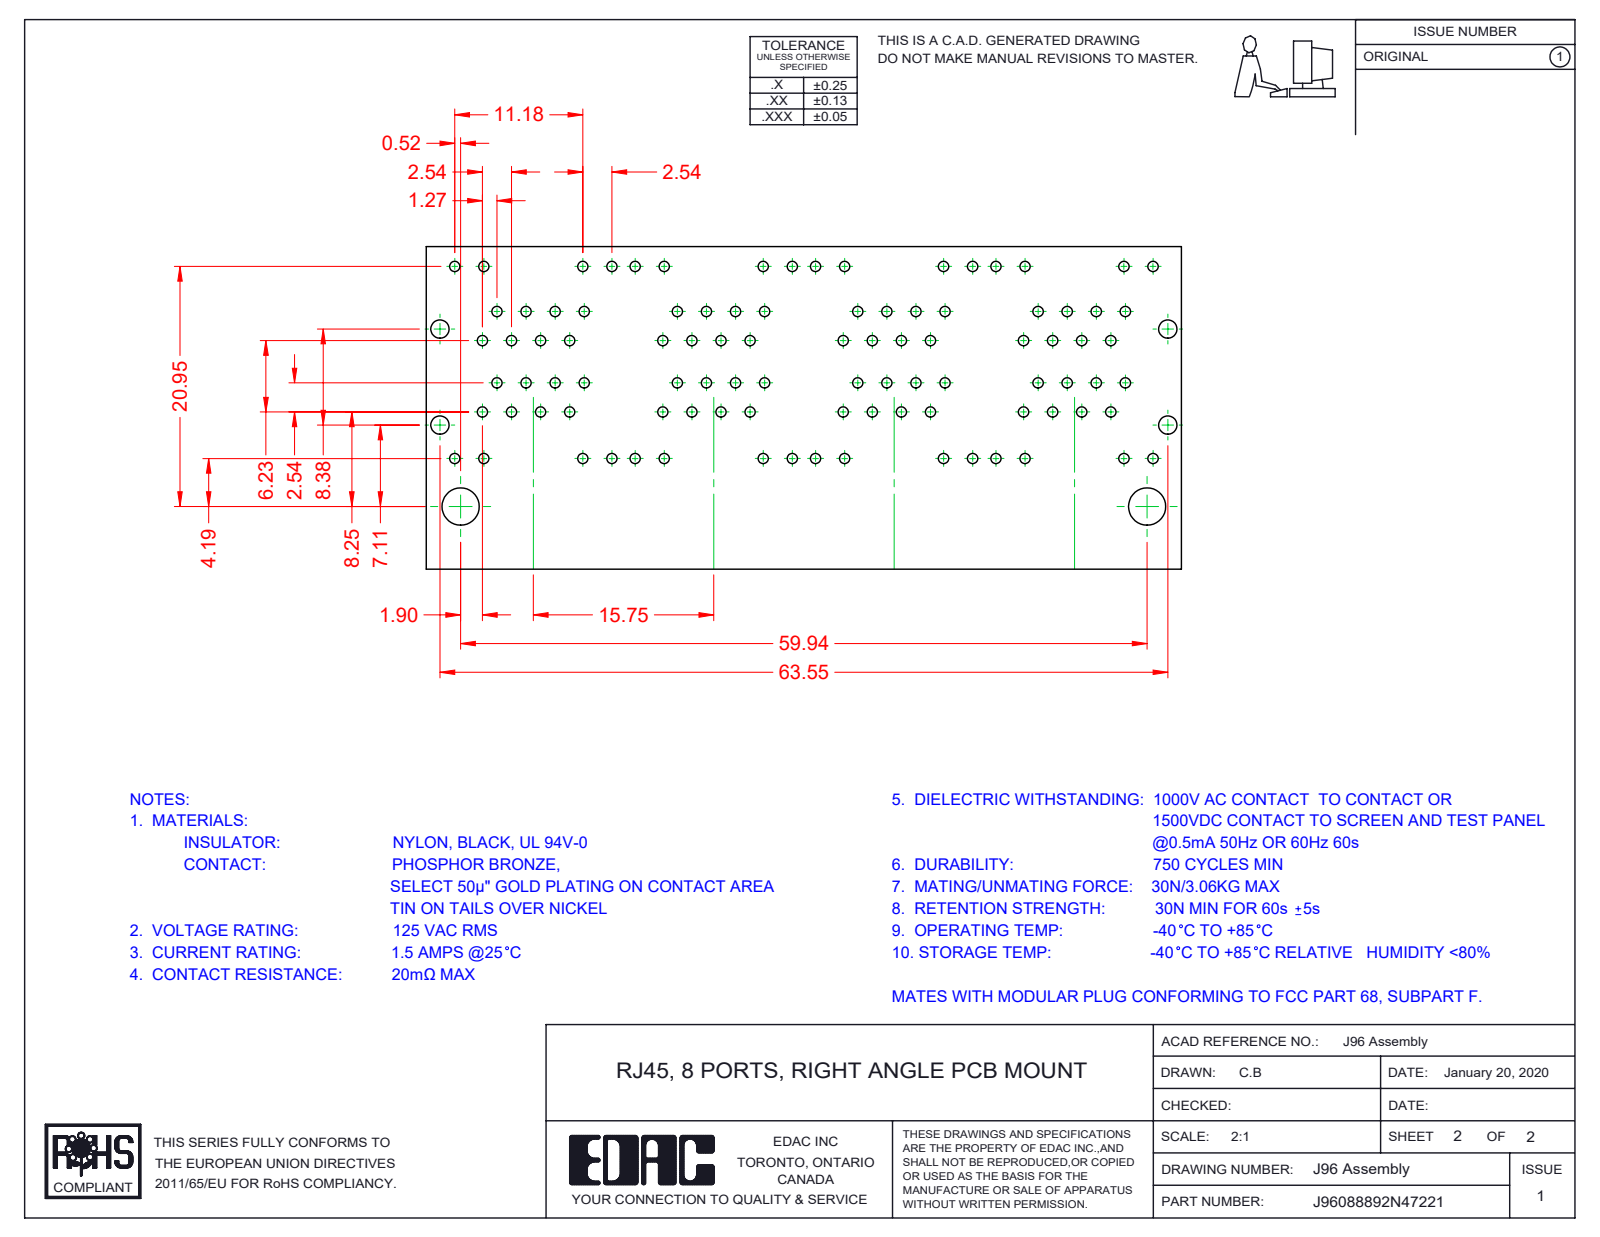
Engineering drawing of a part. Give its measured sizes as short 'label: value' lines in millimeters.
name: 96 Contact Lock Upper; 96 Contacts Upper; 96 Contacts Lower; 96 Contact Lock Lower (+8 more)
written by: SolidWorks 2016 (CONFIG_CONTROL_DESIGN)
unit: mm
bodies: 96 solids, 7820 faces (6105 planar, 1404 cylindrical, 311 other)
size: 67.35 × 31.38 × 28.68
volume: 24 149 mm³; area: 63 596 mm²
holes: 3× ⌀1.7
bosses: 3× ⌀1.68
rounds: 124× R0.25, 73× R0.35, 72× R1, 49× R0.5, 32× R0.91, 27× R0.2, 14× R0.27, 11× R0.7
face distances: 15.75, 0.35, 9.95, 1.17, 1.6, 0.54, 9.98, 10.18, 12.67, 3.37
hole spacings: 15.75, 31.5
